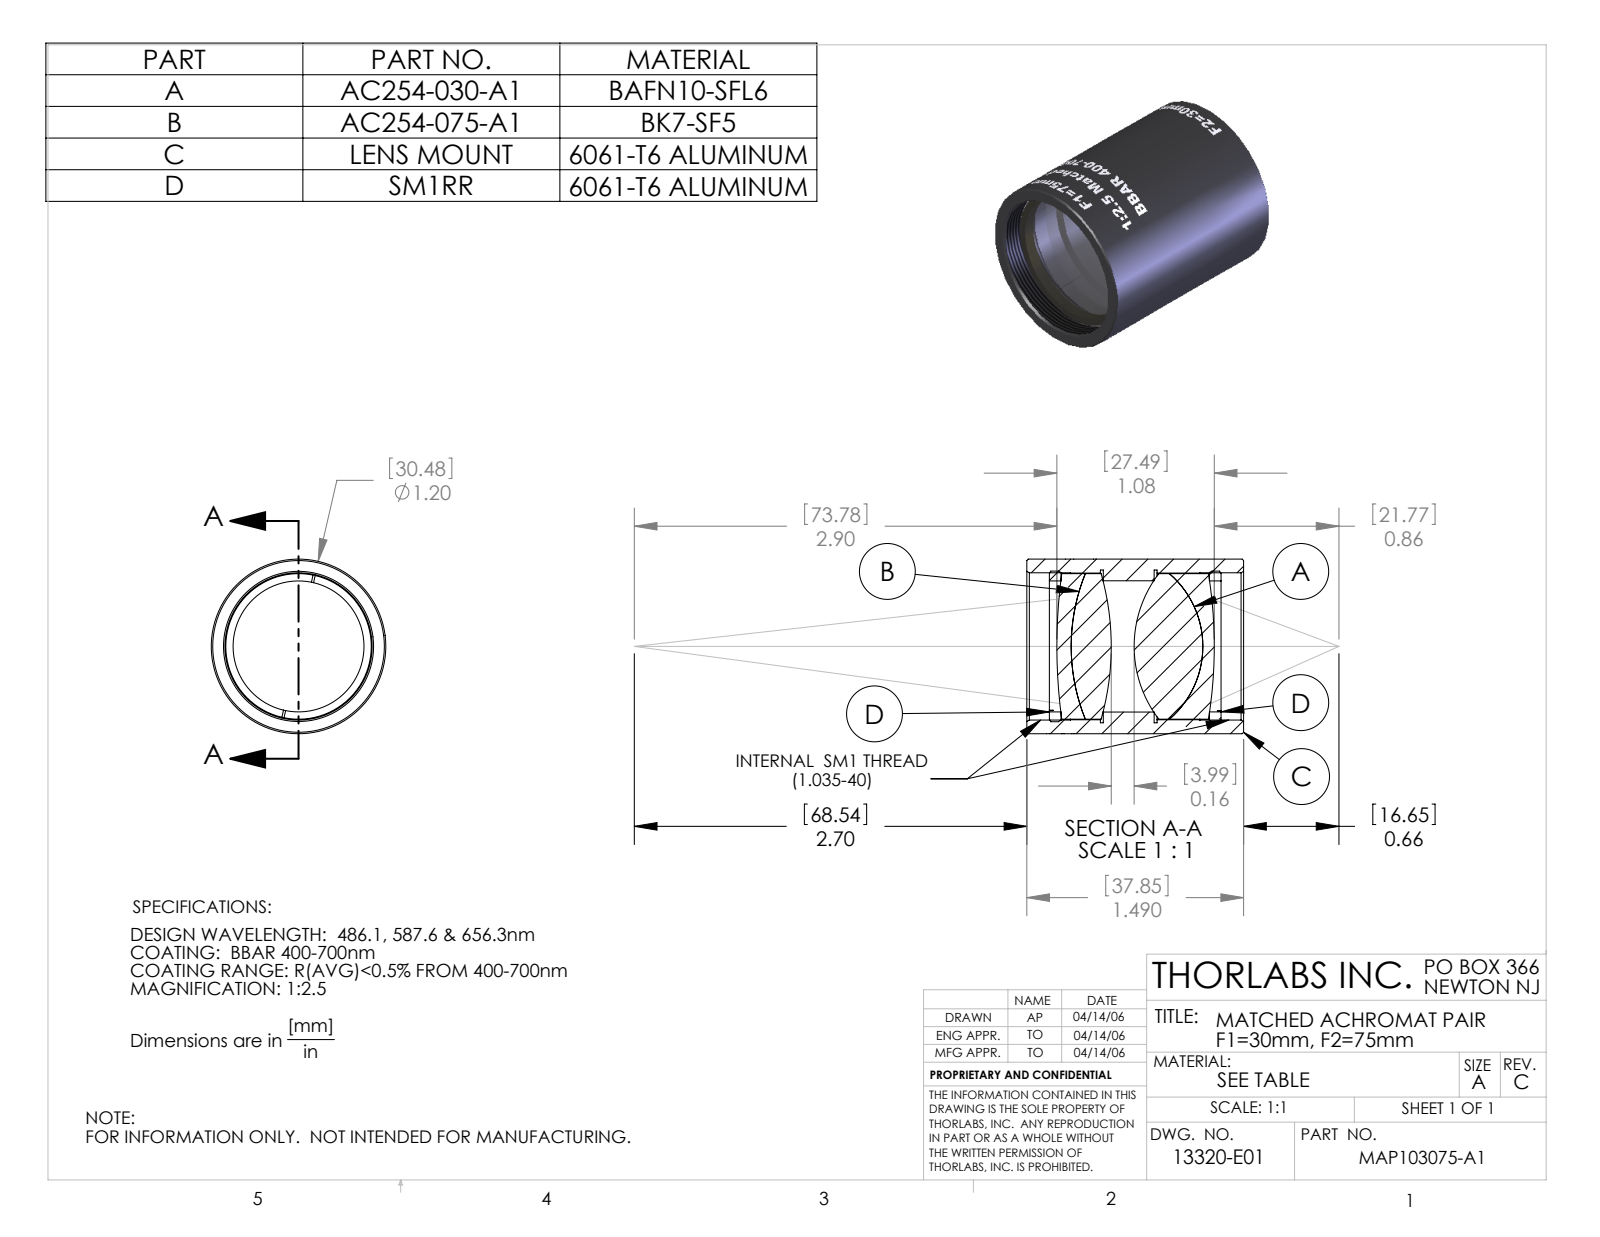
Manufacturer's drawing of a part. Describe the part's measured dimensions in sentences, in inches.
The part is named "13320-E0W". Its 3-D file was written by "SolidWorks 2007 (AUTOMOTIVE_DESIGN)". It is 0 solids with 141 faces: 18 planar, 107 cylindrical and 16 other. Overall it measures 1.49 by 1.2 by 1.2 inches. Round holes: 1 of diameter 0.9, 1 of diameter 1.012. Round bosses or shafts: 1 of diameter 1.2. The main face-to-face distances are 1.49, 1.335, 0.155, 0.155, 1.18, 1.335, 0.015, 0.18, 1.31, 0.025.
